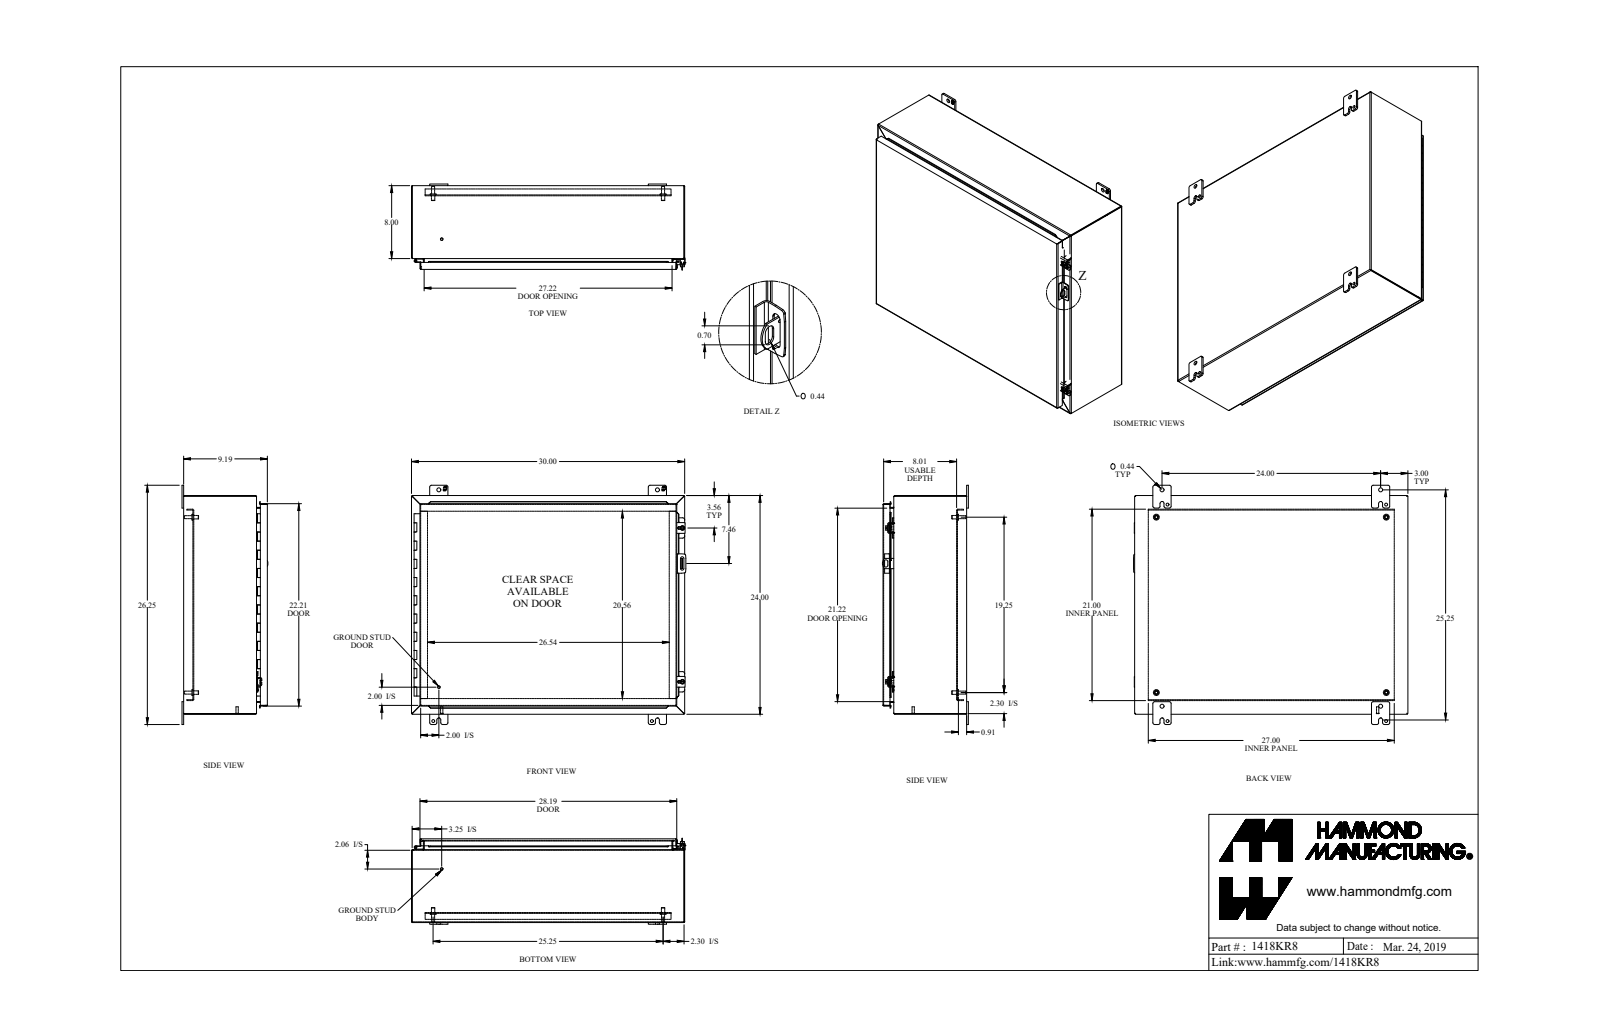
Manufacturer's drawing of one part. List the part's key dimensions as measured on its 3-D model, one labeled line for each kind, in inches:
Part name (STEP PRODUCT): 1418KR8_Default
STEP written by: SolidWorks 2019 (CONFIG_CONTROL_DESIGN)
Units: inches
Bodies: 38 solids, 1156 faces (715 planar, 372 cylindrical, 69 other)
Overall size (bounding box): 30.125 × 26.25 × 9.437
Volume: 262.5 in³ · Surface area: 6 785 in²
Round holes (diameter × count): ⌀0.313 ×4, ⌀0.437 ×4, ⌀0.5 ×4, ⌀0.213 ×2, ⌀0.265 ×2, ⌀0.307 ×2, ⌀0.375 ×2, ⌀0.445 ×2, ⌀0.125 ×1, ⌀0.187 ×1
Round bosses / shafts (diameter × count): ⌀0.65 ×4, ⌀0.375 ×4, ⌀0.33 ×4, ⌀1 ×2, ⌀0.5 ×2, ⌀0.39 ×2, ⌀0.281 ×2, ⌀0.25 ×2
Partial cylindrical surfaces — rounded edges, fillets, slot ends (radius × count): R0.188 ×26, R0.036 ×24, R0.108 ×24, R0.048 ×13, R0.143 ×13, R0.045 ×8, R0.218 ×8, R0.25 ×8
Main face-to-face distances: 0.072, 9.113, 9.041, 9.185, 0.937, 0.095, 1.009, 8.081, 8.009, 1.032
Hole centre spacings: 24, 25.25, 31.751, 33.765, 1.735, 23.75, 27.401, 32.798
